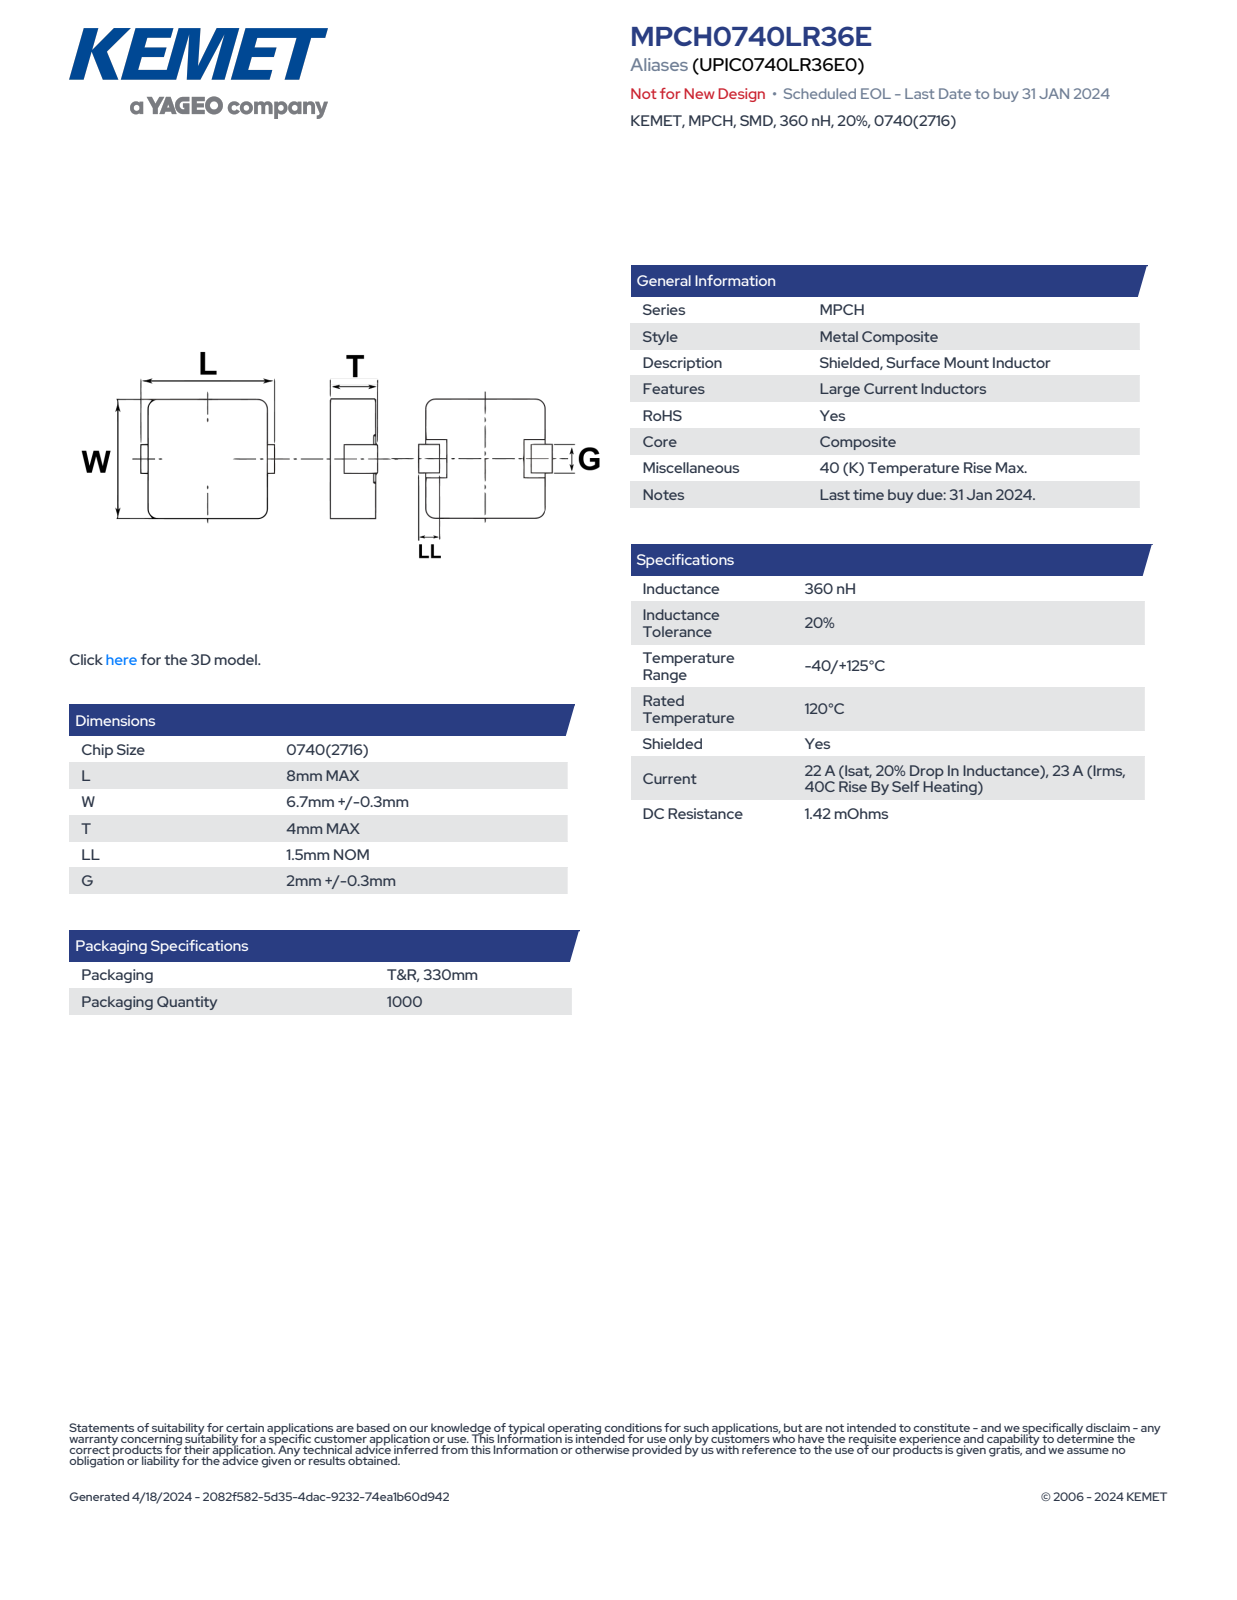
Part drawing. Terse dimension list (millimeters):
name: IS_MPCH_3126_L8W7T4LL1.5G2.3
written by: SolidWorks 2014 (AUTOMOTIVE_DESIGN)
unit: mm
bodies: 4 solids, 105 faces (93 planar, 12 cylindrical, 0 other)
size: 8 × 7 × 4
volume: 210 mm³; area: 250 mm²
rounds: 4× R0.6
face distances: 3.95, 7, 7.59, 7.8, 7.58, 7.6, 7.79, 7.9, 7.69, 7.7
